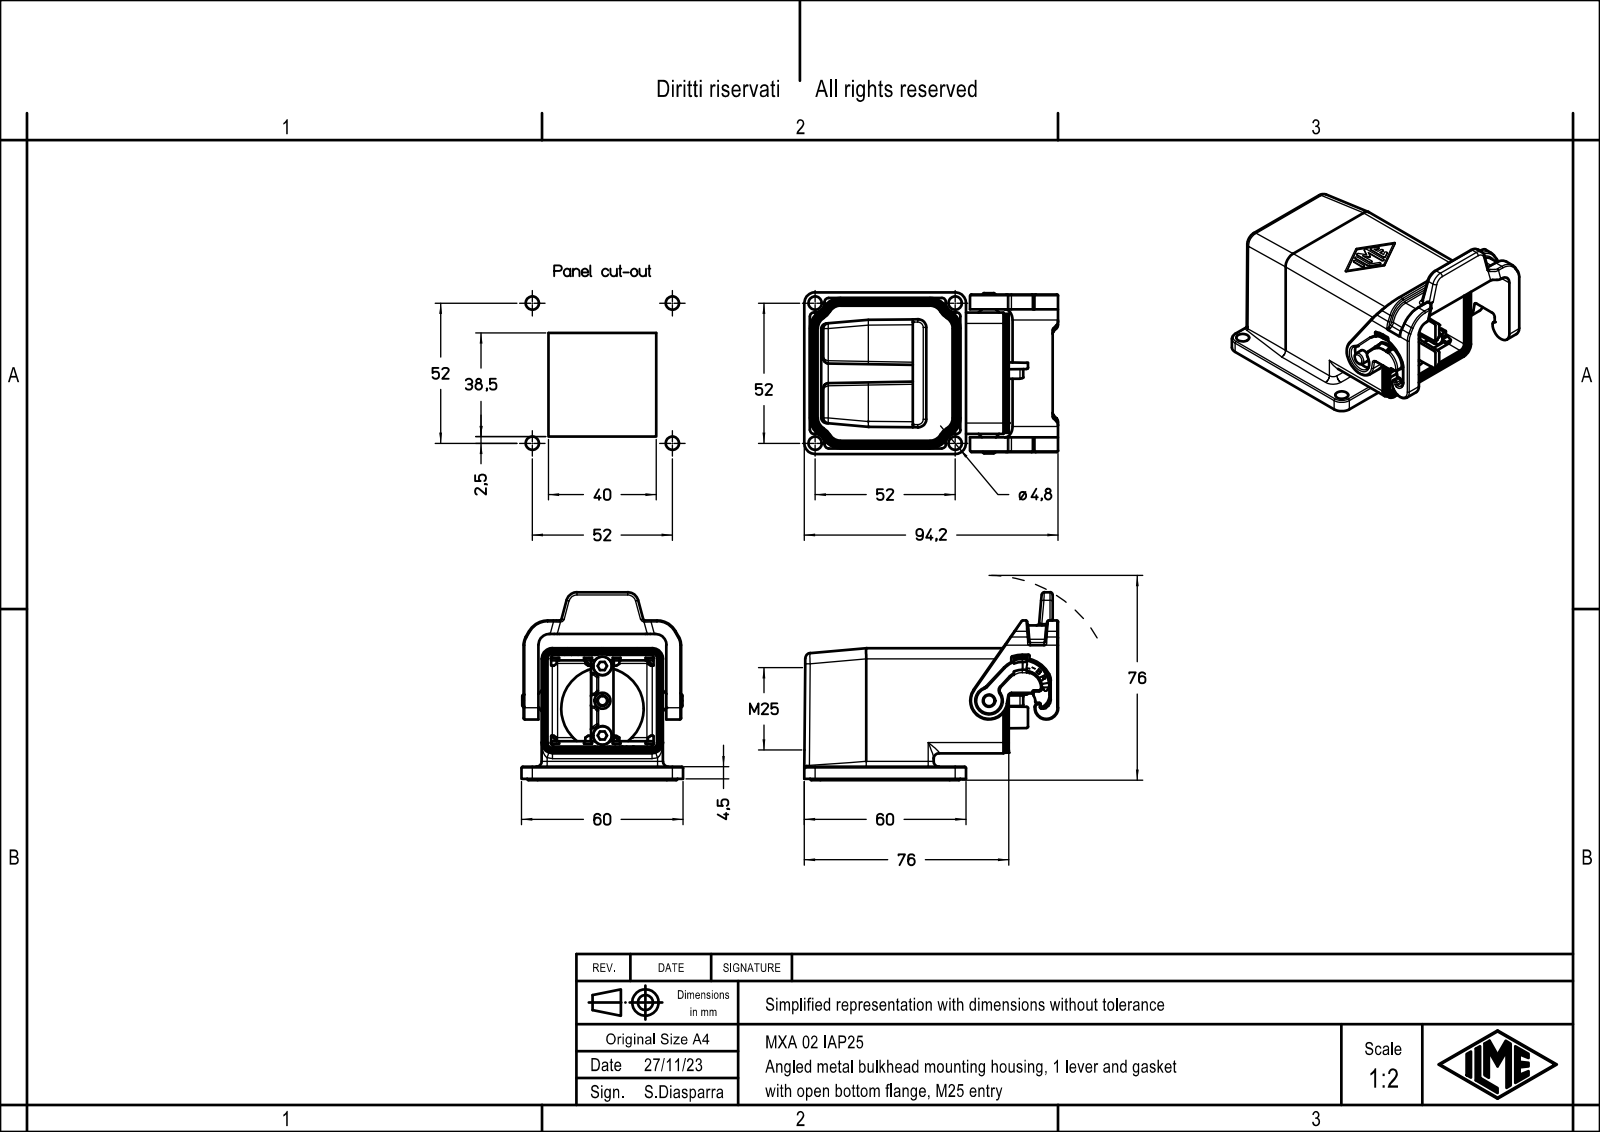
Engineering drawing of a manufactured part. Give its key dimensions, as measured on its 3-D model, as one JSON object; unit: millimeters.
{"part_name": "MXA 02 IAP25", "step_written_by": "Creo Elements/Direct Modeling 20.1B 02-Apr-2019 (C) Parametric Technology GmbH (AUTOMOTIVE_DESIGN)", "units": "millimeters", "bodies": {"solids": 1, "faces": 1698, "planar": 945, "cylindrical": 471, "other": 282}, "overall_size": [94.2, 69.75, 60], "volume_mm3": 61880, "surface_area_mm2": 45735, "round_holes": [[23.6, 1]], "round_bosses_or_shafts": [[7, 2], [4, 2], [6, 1], [3.6, 1]], "partial_cylinders_radius": [[0.5, 101], [0.1, 45], [1, 32], [2, 26], [1.5, 22], [0.3, 16], [4.5, 16], [0.2, 15]], "face_to_face_distances": [45, 1.25, 53, 5, 48.5, 4.5, 46.25, 44, 2.5, 36.5]}
